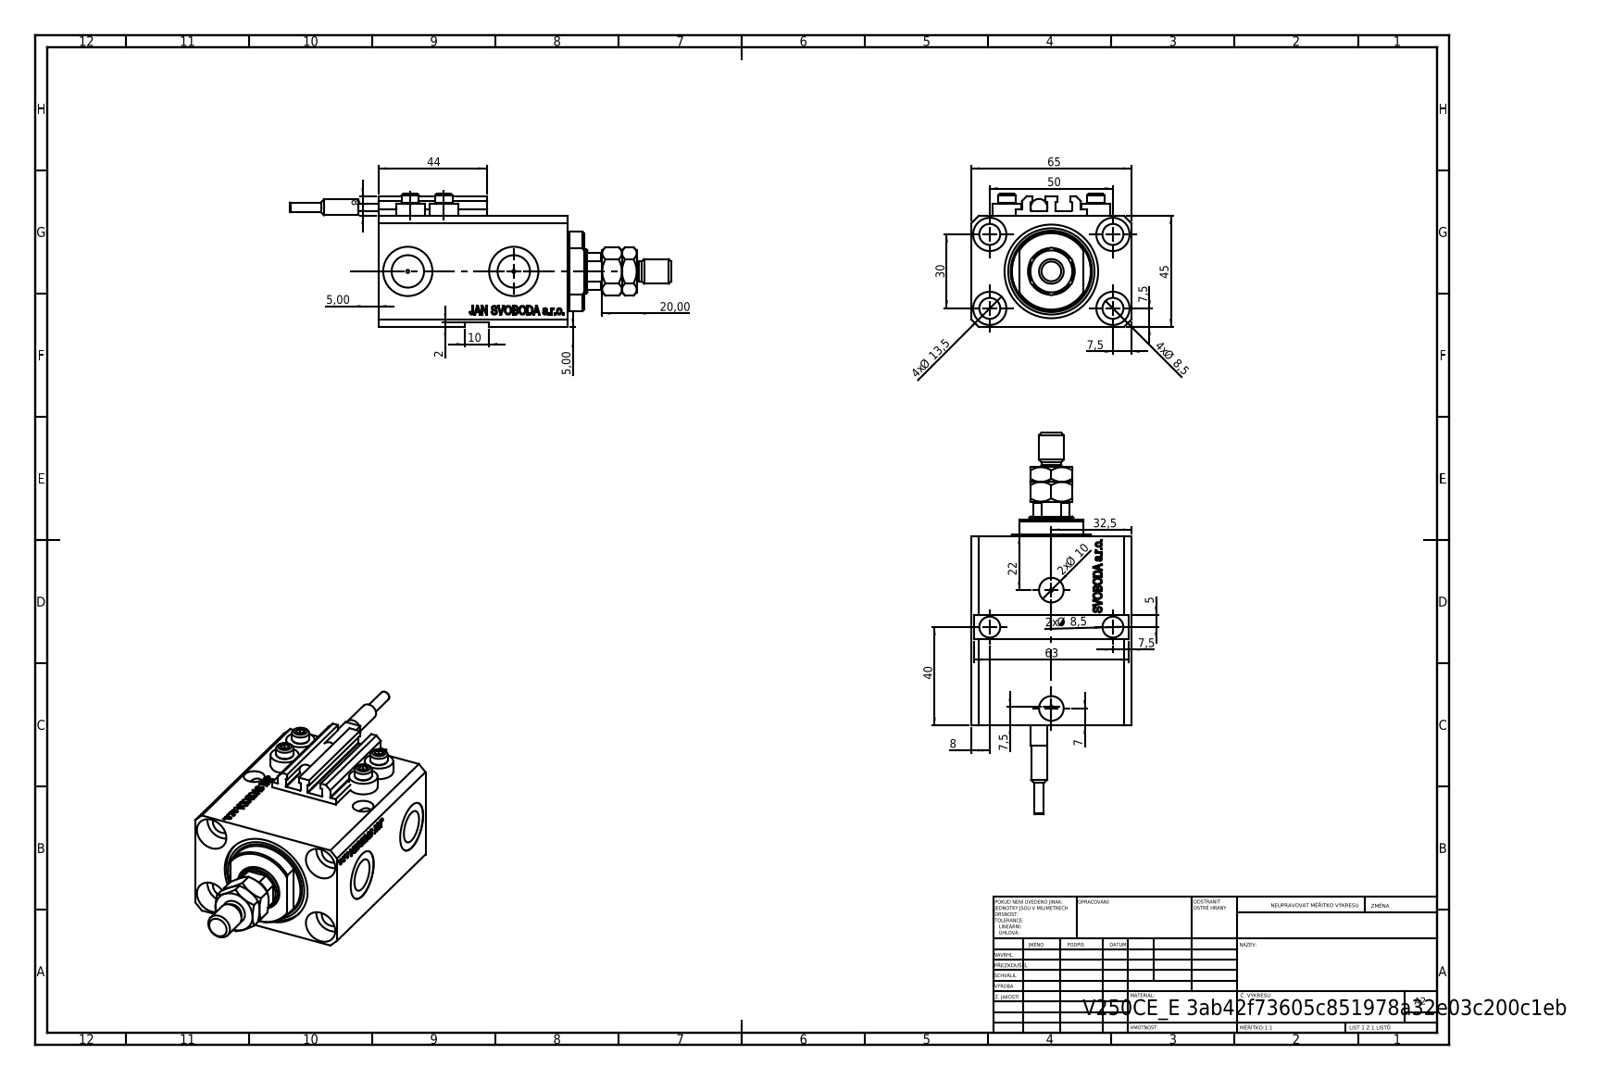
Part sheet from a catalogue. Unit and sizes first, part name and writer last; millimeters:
Units: millimetres
Overall size (bounding box): 154.9 × 65 × 54
Round holes (diameter × count): ⌀8.5 ×7, ⌀1.25 ×4, ⌀4 ×4, ⌀13.5 ×4, ⌀10 ×2, ⌀13.16 ×2, ⌀20 ×2, ⌀18 ×1, ⌀25 ×1, ⌀38 ×1
Round bosses / shafts (diameter × count): ⌀11.6 ×4, ⌀7 ×4, ⌀10 ×1, ⌀8 ×1, ⌀6.8 ×1, ⌀6.5 ×1, ⌀4 ×1
Partial cylindrical surfaces — rounded edges, fillets, slot ends (radius × count): R0.2 ×10, R8.5 ×1, R16 ×1
Main face-to-face distances: 45, 65, 51.9, 25.1, 6.9, 77, 2, 3, 70.1, 47
Hole centre spacings: 29.15, 50, 13.6, 15.12, 18.81, 18.97, 26.22, 26.61
Volume: 202 430 mm³ · Surface area: 65 515 mm²
Bodies: 10 solids, 1158 faces (546 planar, 148 cylindrical, 464 other)
Part name (STEP PRODUCT): V250CE_C_VCP; V250CE_E; SWITCH_V250CE; MTA (+2 more)
STEP written by: SolidWorks 2019 (CONFIG_CONTROL_DESIGN)
